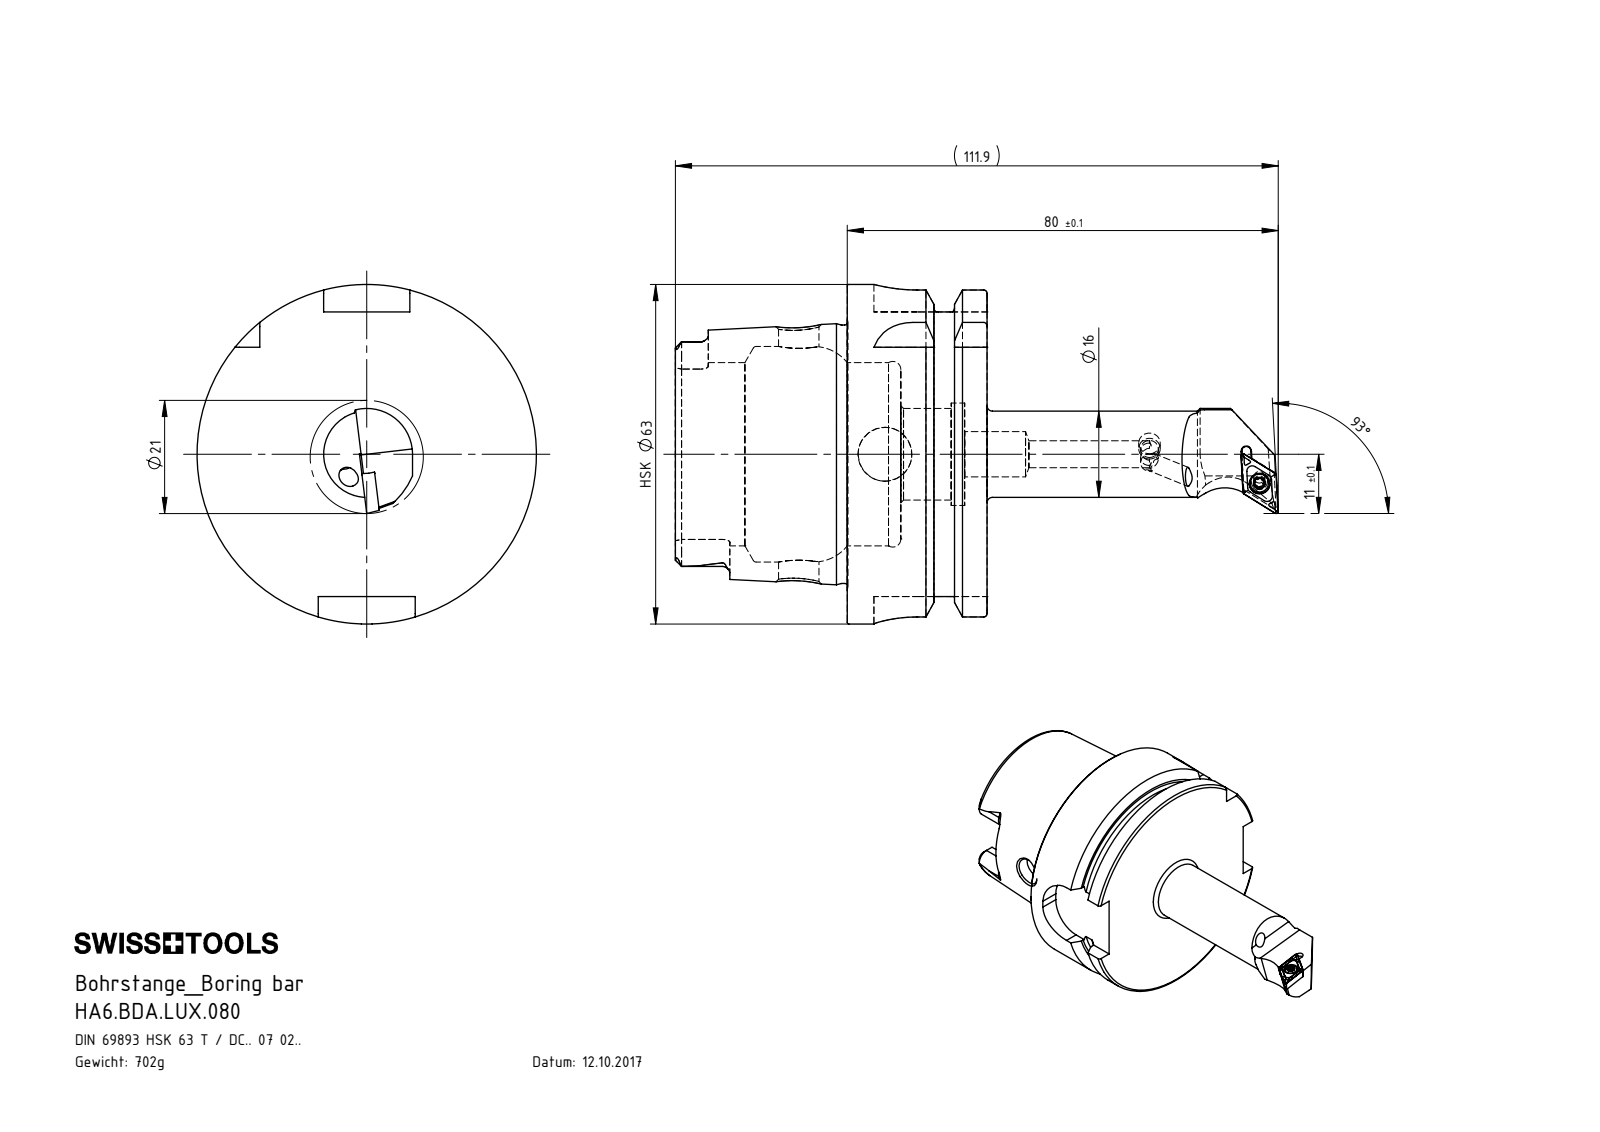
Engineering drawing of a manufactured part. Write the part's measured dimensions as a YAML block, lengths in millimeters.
part_name: "HA6-BDA.LUX.080_A; DCMT070204; WCA-ER2.001.006_B; KVT_MB_600_040 (+1 more)"
step_written_by: "SolidWorks 2017 (AUTOMOTIVE_DESIGN)"
units: millimeters
bodies: {solids: 5, faces: 314, planar: 82, cylindrical: 93, other: 139}
overall_size: [111.89, 63, 63]
volume: 89542
surface_area: 25920
round_holes:
  - {diameter: 3.3, count: 2}
  - {diameter: 2.05, count: 1}
  - {diameter: 2.8, count: 1}
  - {diameter: 3, count: 1}
  - {diameter: 3.85, count: 1}
  - {diameter: 4, count: 1}
  - {diameter: 5, count: 1}
  - {diameter: 7.5, count: 1}
  - {diameter: 8.4, count: 1}
  - {diameter: 10, count: 1}
  - {diameter: 17, count: 1}
  - {diameter: 19, count: 1}
round_bosses_or_shafts:
  - {diameter: 63, count: 1}
  - {diameter: 54.95, count: 1}
  - {diameter: 47.94, count: 1}
  - {diameter: 16, count: 1}
  - {diameter: 4, count: 1}
  - {diameter: 3.4, count: 1}
  - {diameter: 2.5, count: 1}
partial_cylinders:
  - {radius: 0.21, count: 6}
  - {radius: 1.4, count: 6}
  - {radius: 0.36, count: 5}
  - {radius: 8, count: 4}
  - {radius: 2.82, count: 2}
  - {radius: 2.88, count: 2}
  - {radius: 0.36, count: 1}
  - {radius: 0.85, count: 1}
face_to_face_distances: [25.95, 16, 9.95, 31.9, 41.85, 57.85, 52.8, 21.8, 11.85, 53.7]
